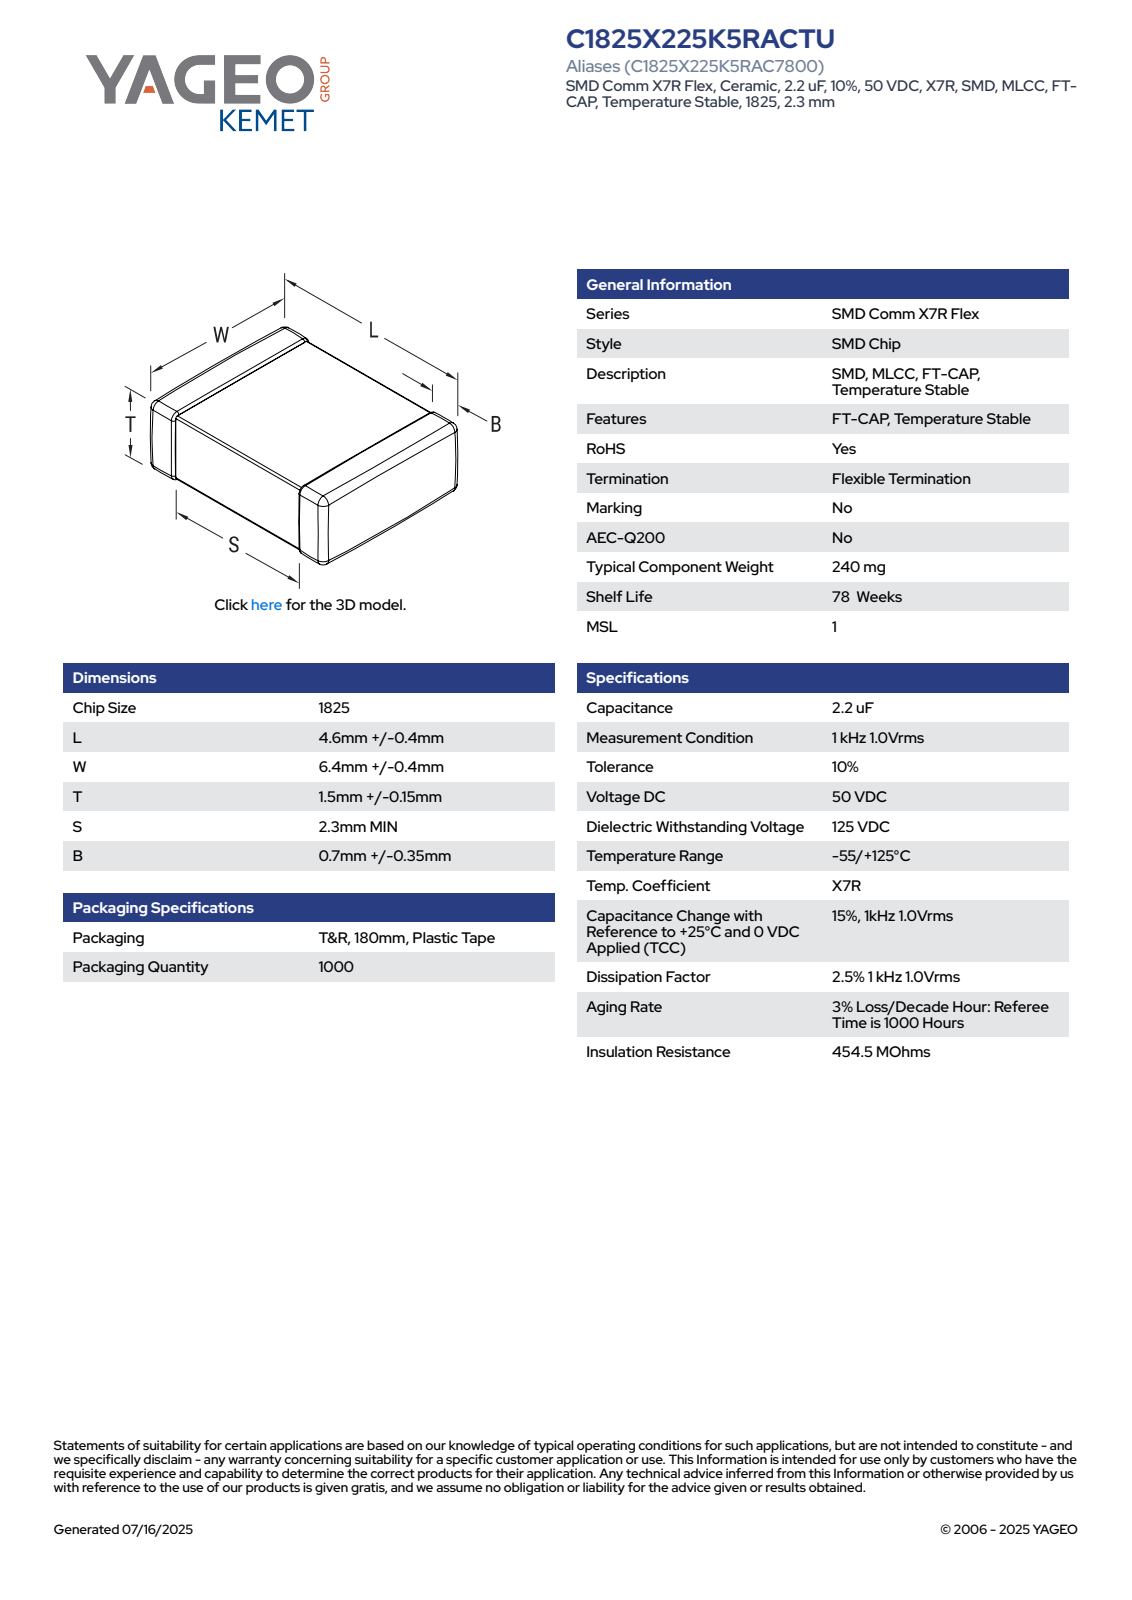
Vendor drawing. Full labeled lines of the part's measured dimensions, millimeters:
Part name (STEP PRODUCT): CCS_CCSTDNOS_1825_L5W6.8T1.65B1.05
STEP written by: SolidWorks 2014 (AUTOMOTIVE_DESIGN)
Units: millimetres
Bodies: 4 solids, 121 faces (71 planar, 34 cylindrical, 16 other)
Overall size (bounding box): 6.8 × 5 × 1.65
Volume: 49 mm³ · Surface area: 104 mm²
Partial cylindrical surfaces — rounded edges, fillets, slot ends (radius × count): R0.14 ×24
Main face-to-face distances: 1.51, 1.37, 1.65, 5, 6.66, 6.52, 6.8, 3.54, 3.12, 0.36
